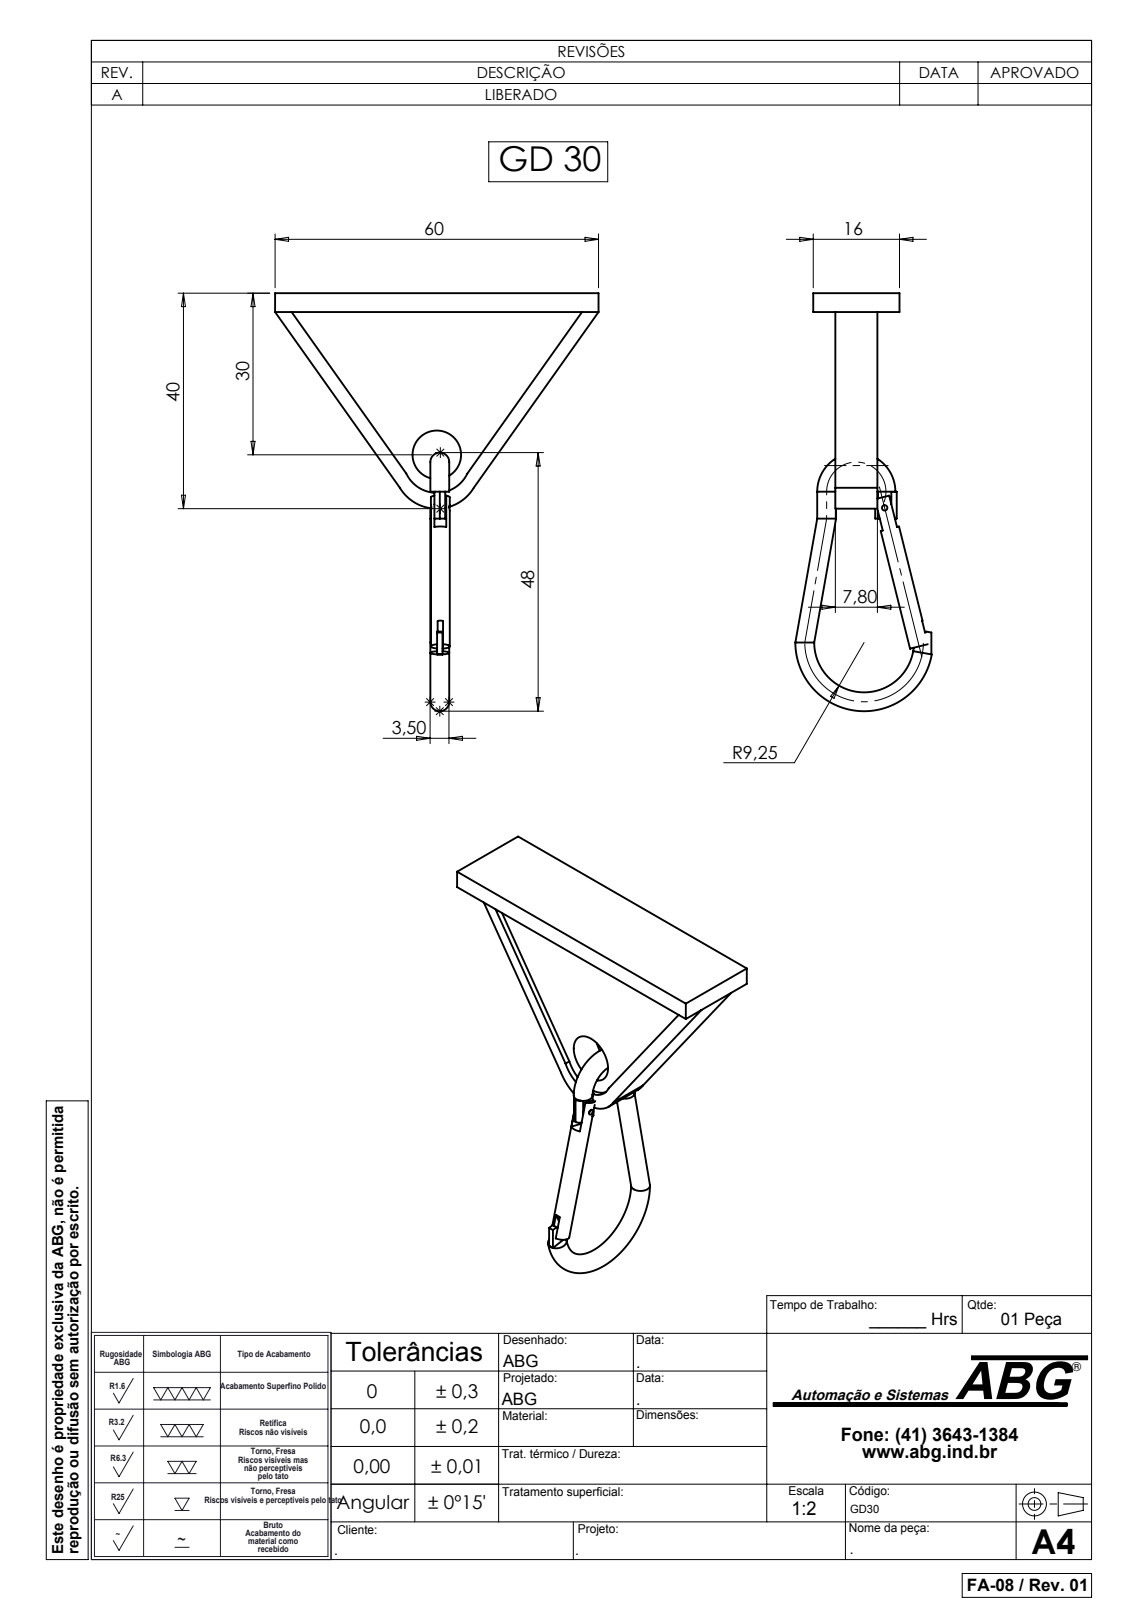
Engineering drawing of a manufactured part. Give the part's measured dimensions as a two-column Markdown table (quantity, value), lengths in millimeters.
| quantity | value |
| --- | --- |
| part name | Gancho 2; Gancho Deslizante; GD30; Gancho 1 |
| STEP written by | SolidWorks 2007 (CONFIG_CONTROL_DESIGN) |
| units | millimeters |
| bodies | 3 solids, 75 faces (46 planar, 19 cylindrical, 10 other) |
| overall size | 77.6 × 60 × 25.31 |
| volume | 11 668 mm³ |
| surface area | 6 852 mm² |
| round holes (diameter × count) | 1 × 1, 9 × 1 |
| round bosses / shafts (diameter × count) | 3.5 × 2 |
| partial cylindrical surfaces (radius × count) | 0.5 × 2, 1 × 1, 6.26 × 1, 8 × 1 |
| main face-to-face distances | 5.8, 3.5, 1, 6.8, 4.1, 5.1, 10.9, 11.9, 7.8, 16 |
